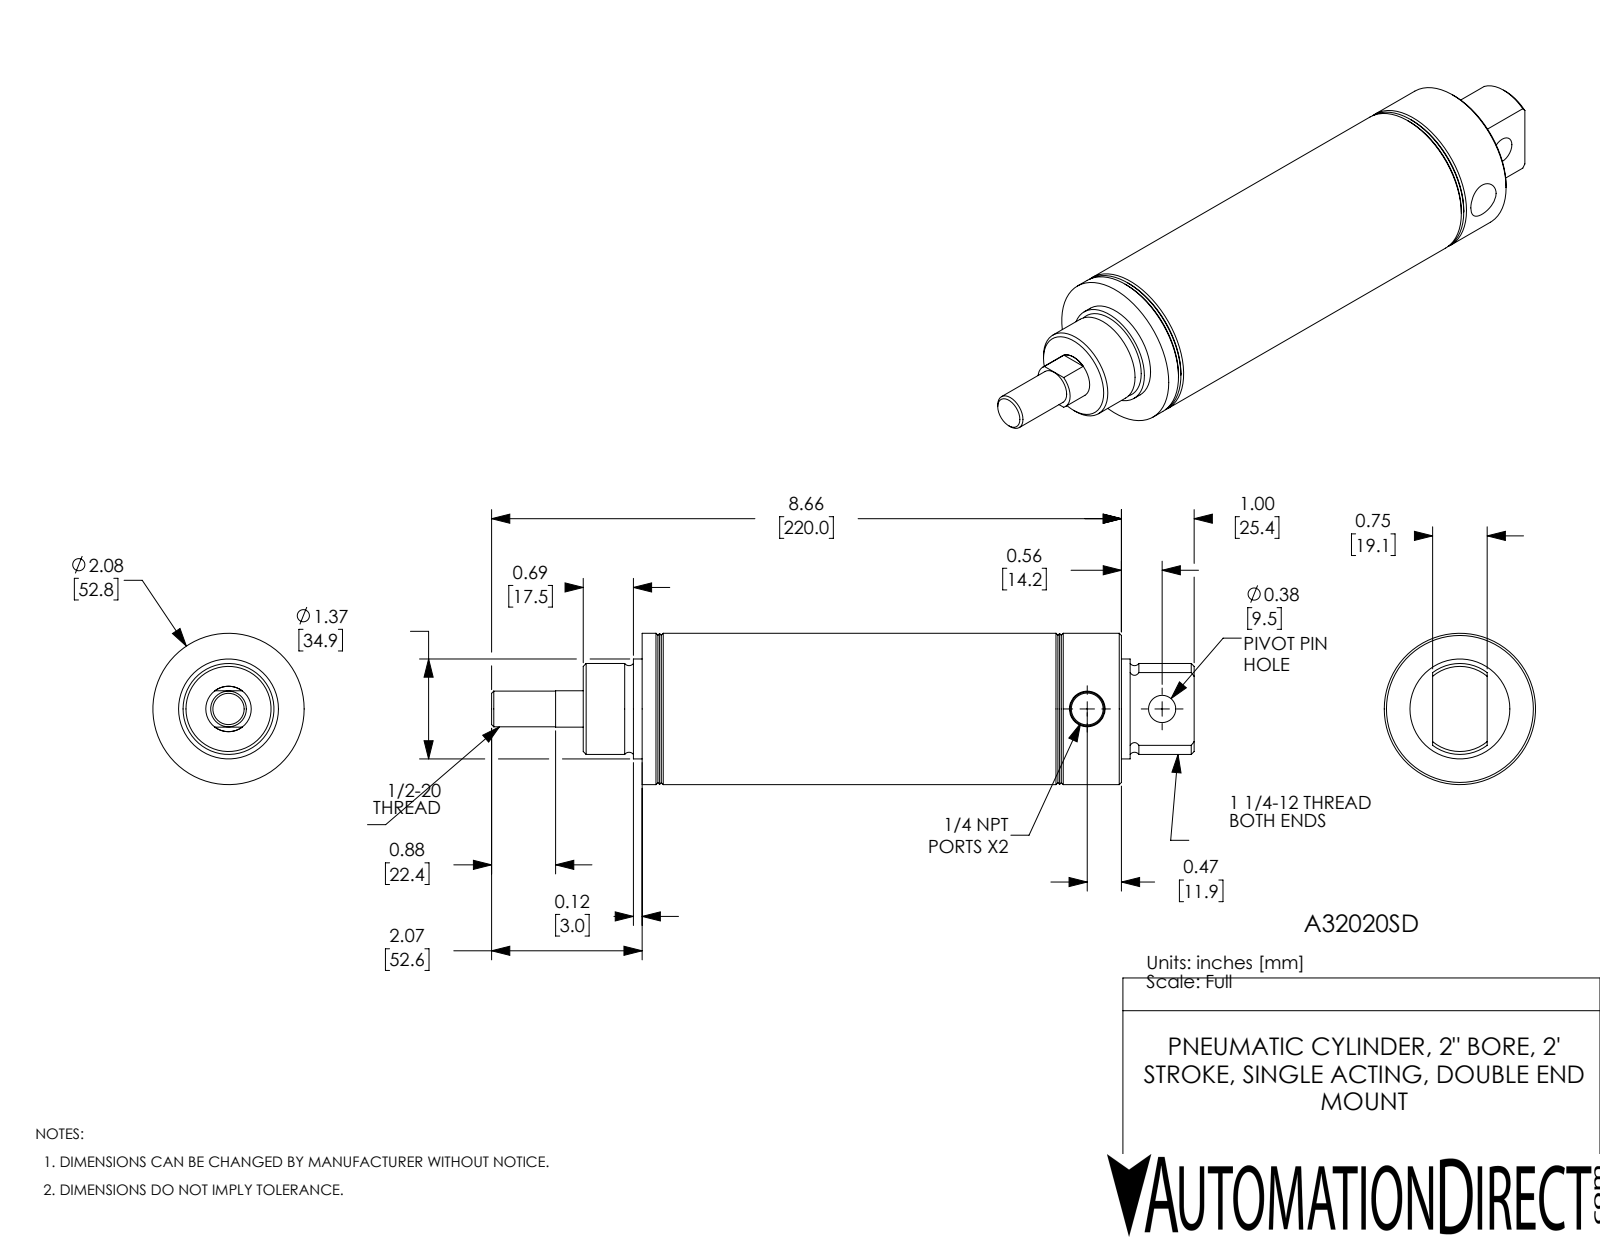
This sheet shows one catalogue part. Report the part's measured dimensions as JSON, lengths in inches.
{"part_name": "A32020SD; A32020SD-MainBody; A32020SD-Rod", "step_written_by": "SolidWorks 2017 (AUTOMOTIVE_DESIGN)", "units": "inches", "bodies": {"solids": 2, "faces": 83, "planar": 19, "cylindrical": 28, "other": 36}, "overall_size": [9.66, 2.08, 2.08], "volume_in3": 18.73, "surface_area_in2": 106.7, "round_holes": [[0.375, 1], [0.438, 1], [0.625, 1], [2, 1]], "round_bosses_or_shafts": [[2.08, 1], [1.373, 1], [1.25, 1], [0.491, 1]], "face_to_face_distances": [2.045, 4.545, 0.5, 2.5, 2, 4.045, 2.545, 6.59, 0.12, 2.165], "hole_center_spacings": [1.03]}
